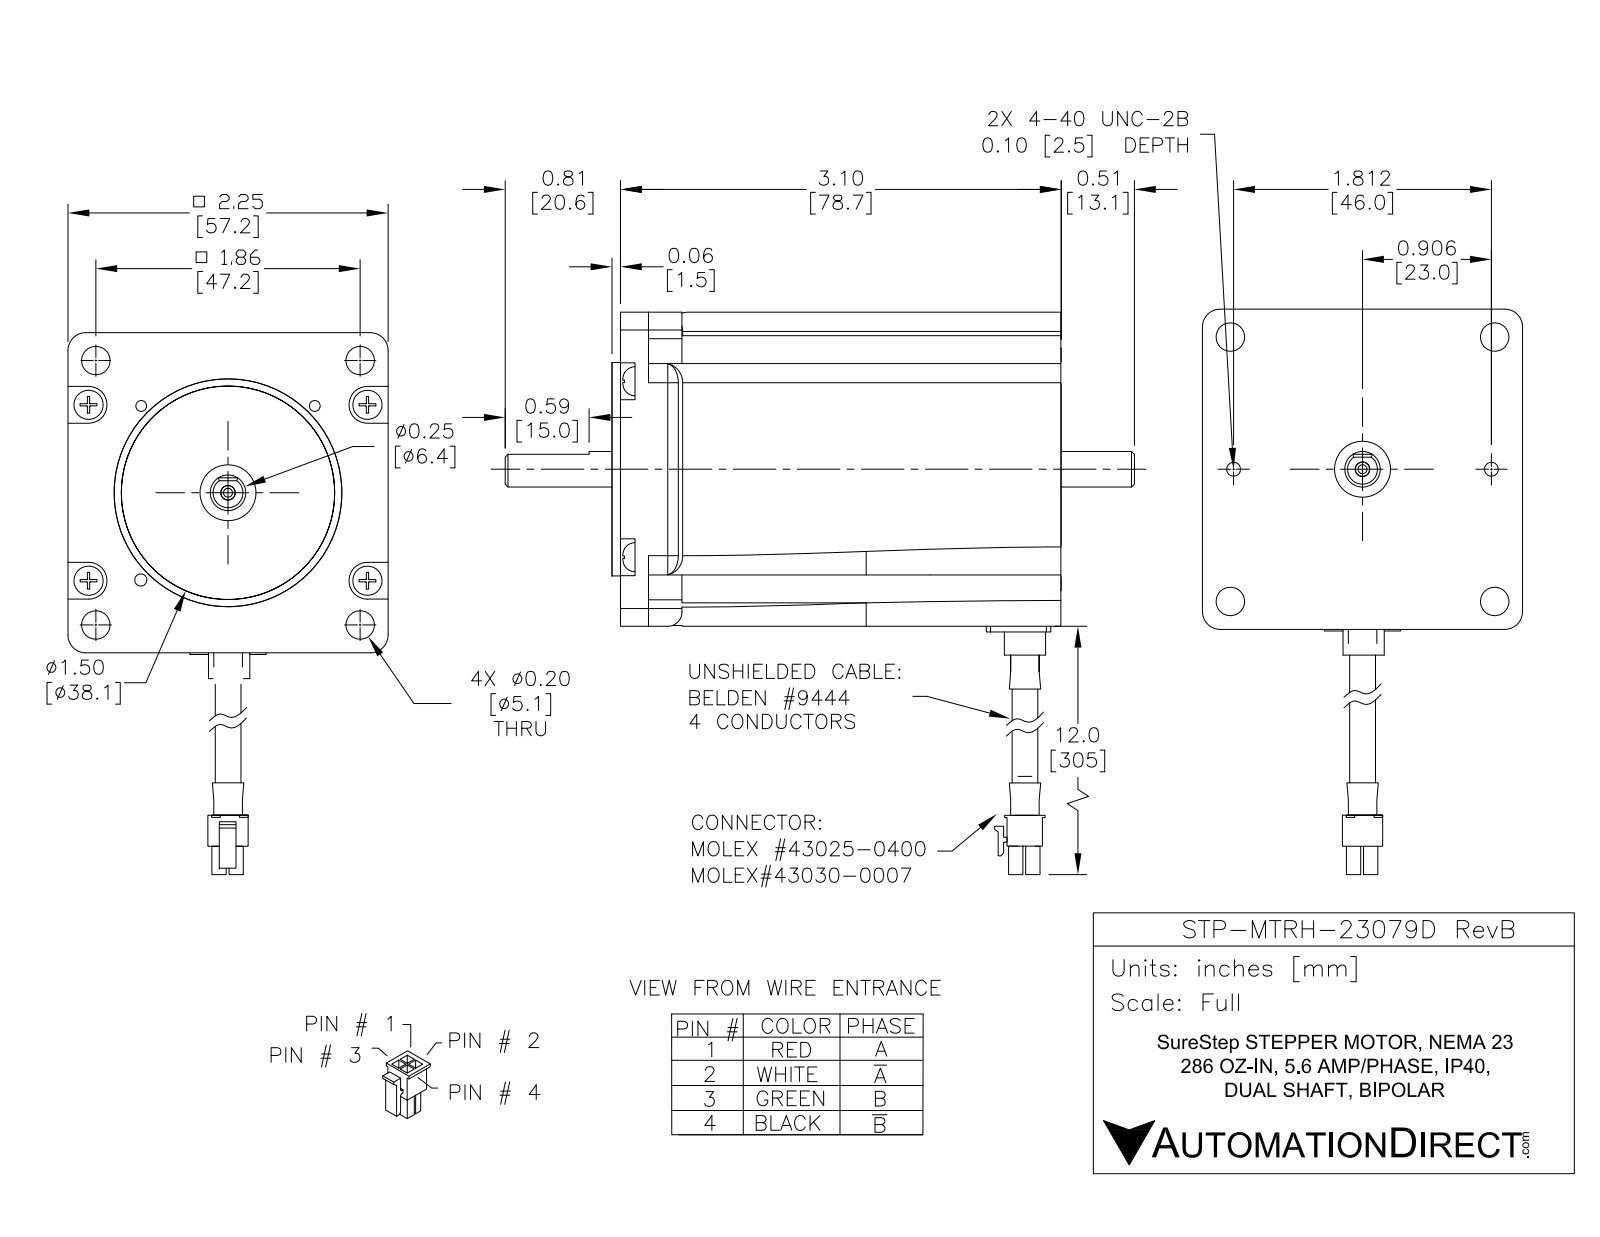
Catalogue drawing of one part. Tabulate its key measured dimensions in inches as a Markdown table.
| quantity | value |
| --- | --- |
| part name | STP-MTRH-23079D |
| STEP written by | SolidWorks 2017 (AUTOMOTIVE_DESIGN) |
| units | inches |
| bodies | 4 solids, 498 faces (328 planar, 112 cylindrical, 58 other) |
| overall size | 14.523 × 4.422 × 2.207 |
| volume | 12.93 in³ |
| surface area | 62.17 in² |
| round holes (diameter × count) | 0.097 × 4, 0.2 × 4, 0.085 × 2, 0.125 × 2, 0.125 × 2, 0.063 × 1, 0.25 × 1, 0.394 × 1, 0.398 × 1, 0.465 × 1, 1.6 × 1, 2.152 × 1 |
| round bosses / shafts (diameter × count) | 1.7 × 1, 1.5 × 1, 0.29 × 1, 0.25 × 1, 0.217 × 1 |
| partial cylindrical surfaces (radius × count) | 0.125 × 10, 0.03 × 4, 0.129 × 4, 0.175 × 4, 0.196 × 4, 0.013 × 3, 0.059 × 2, 0.006 × 1 |
| main face-to-face distances | 2.207, 0.314, 2.014, 1.7, 1.083, 1.398, 3.098, 1.081, 1.395, 3.095 |
| hole center spacings | 0.316, 0.622, 1.159, 1.181, 1.314, 1.553, 1.649, 1.828 |
